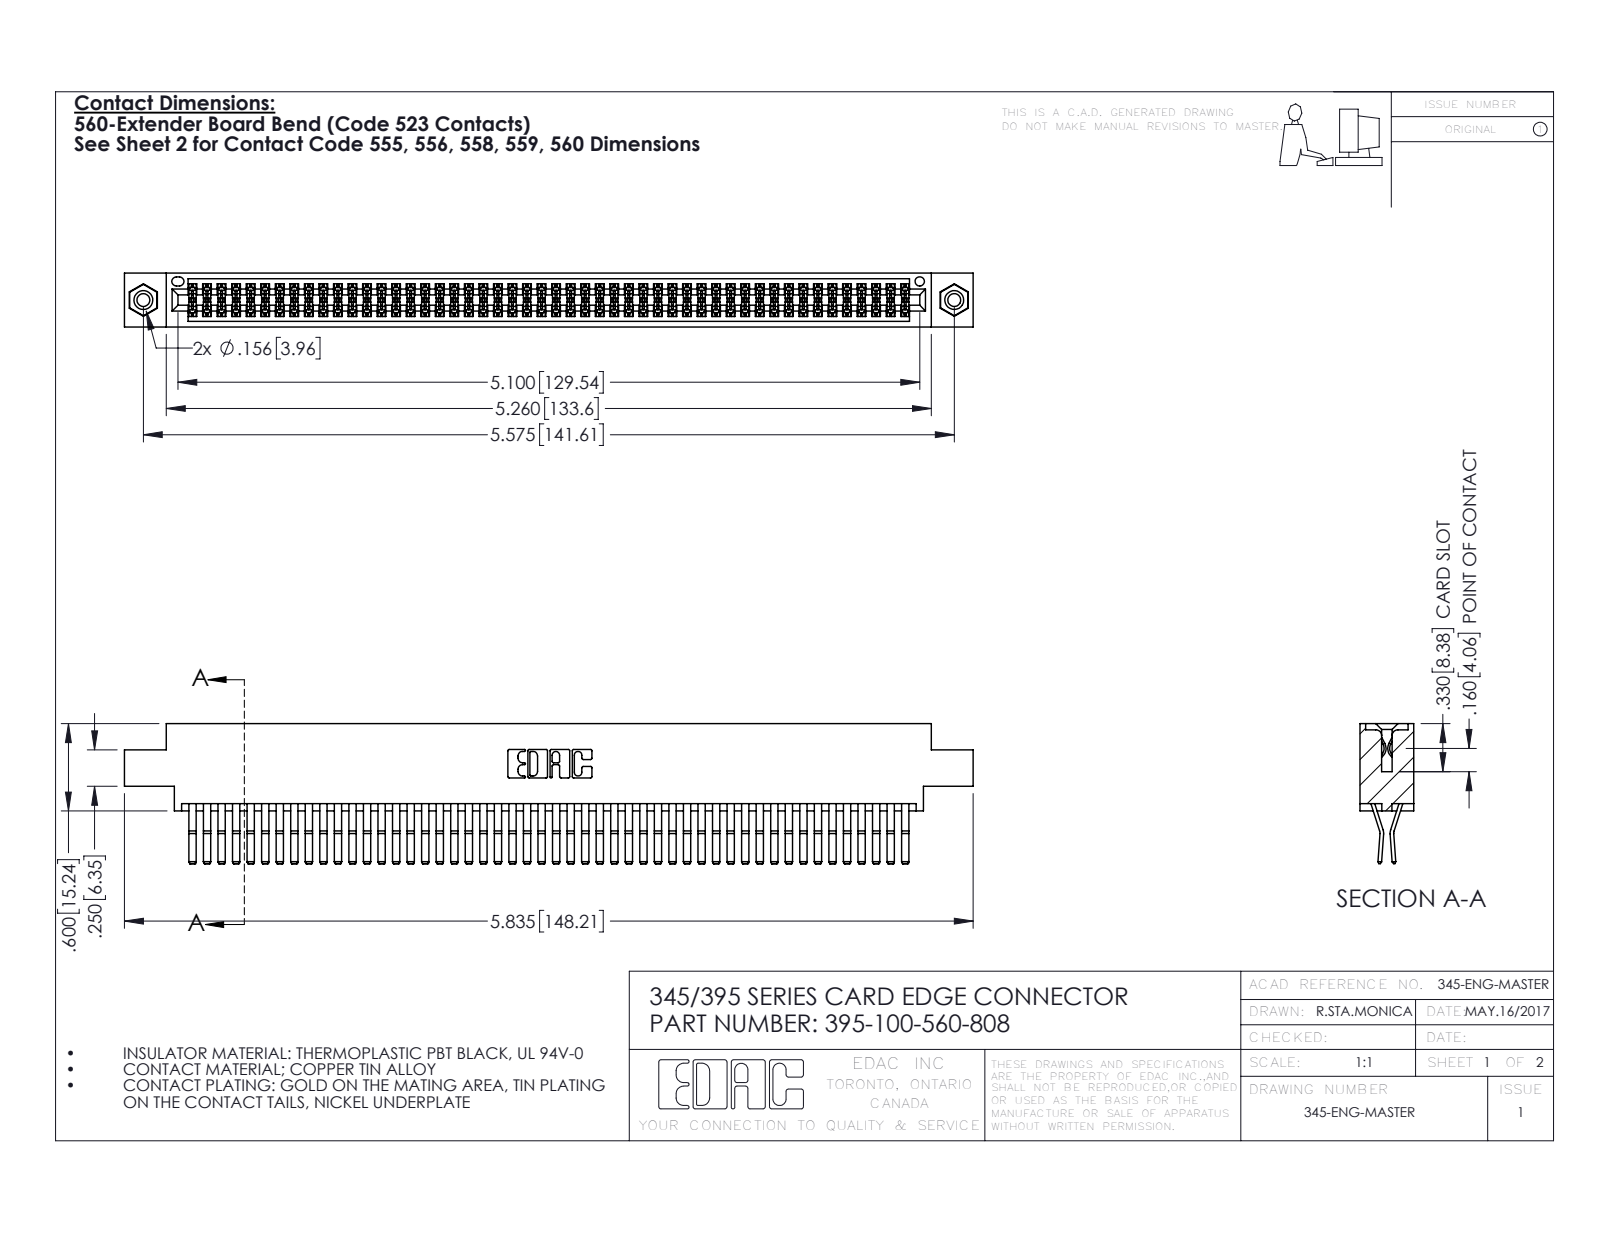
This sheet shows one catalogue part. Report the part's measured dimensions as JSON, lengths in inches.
{"part_name": "345-250-001_345-250-003-102; 345 Part_0.170 Offset - 0.156 Dia-TI; 395-100-560-808; 345-292-001_560 Tail", "step_written_by": "SolidWorks 2016 (CONFIG_CONTROL_DESIGN)", "units": "inches", "bodies": {"solids": 103, "faces": 5390, "planar": 3416, "cylindrical": 1958, "other": 16}, "overall_size": [5.835, 0.962, 0.37], "volume_in3": 0.916, "surface_area_in2": 37.48, "round_holes": [[0.089, 2], [0.125, 2], [0.156, 2], [0.064, 1]], "round_bosses_or_shafts": [[0.155, 2]], "partial_cylinders_radius": [[0.006, 151], [0.01, 22], [0.007, 6], [0.031, 6], [0.026, 3], [0.01, 2], [0.014, 2], [0.019, 2]], "face_to_face_distances": [0.025, 0.072, 0.298, 0.37, 0.2, 0.098, 0.272, 0.225, 0.175, 0.149], "hole_center_spacings": [0.27, 5.339, 5.575]}
